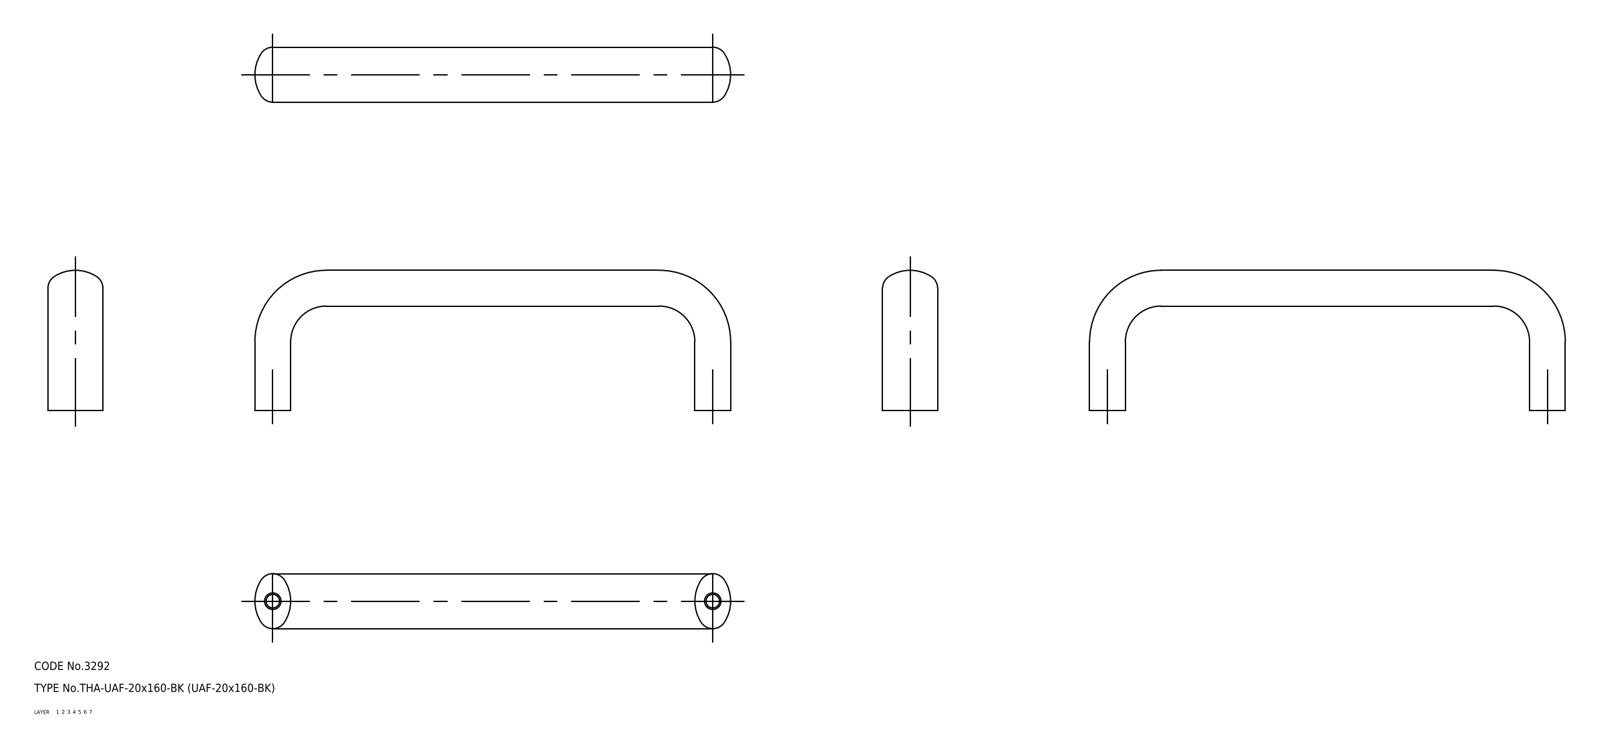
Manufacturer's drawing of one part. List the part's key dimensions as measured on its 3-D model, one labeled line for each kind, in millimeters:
Part name (STEP PRODUCT): pull
STEP written by: CADfix (AUTOMOTIVE_DESIGN)
Units: millimetres
Bodies: 1 solid, 18 faces (0 planar, 0 cylindrical, 18 other)
Overall size (bounding box): 173 × 51 × 20
Volume: 46 801 mm³ · Surface area: 12 955 mm²
